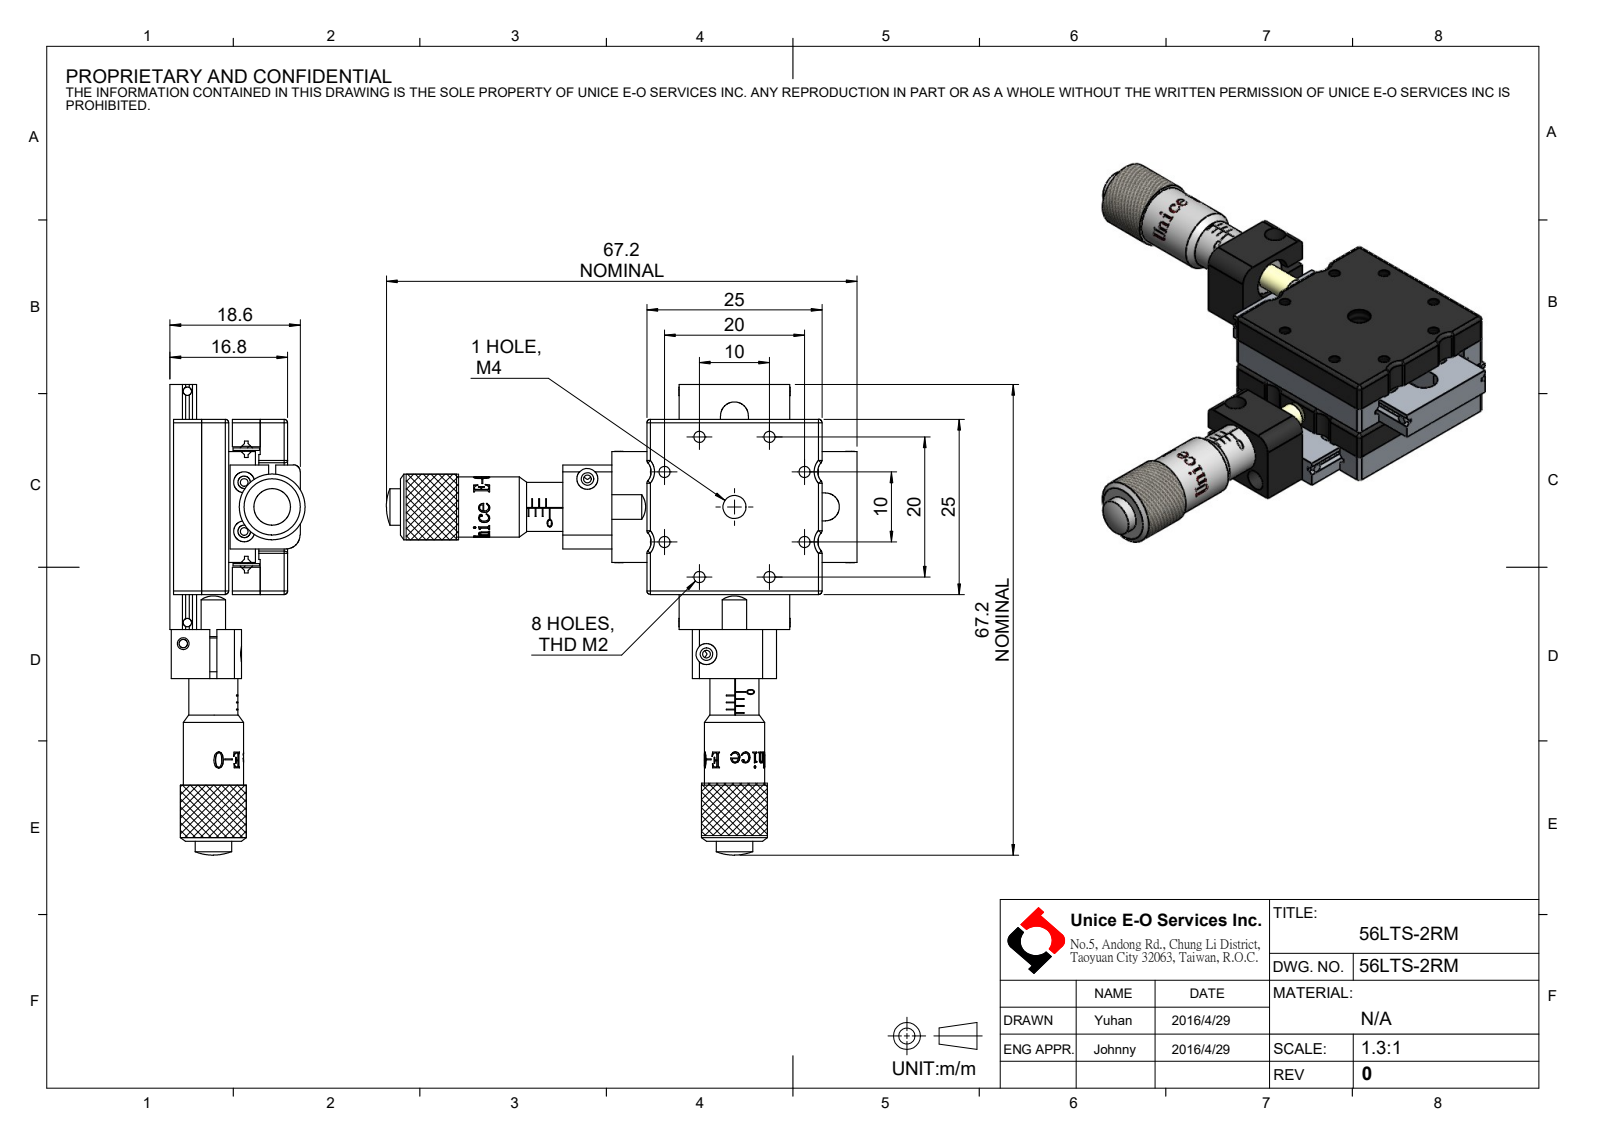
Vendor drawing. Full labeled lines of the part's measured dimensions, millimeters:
Part name (STEP PRODUCT): 56LTS-2RM
STEP written by: SolidWorks 2016 (CONFIG_CONTROL_DESIGN)
Units: millimetres
Bodies: 42 solids, 1664 faces (666 planar, 622 cylindrical, 376 other)
Overall size (bounding box): 67.2 × 67.2 × 19.3
Volume: 13 403 mm³ · Surface area: 16 109 mm²
Round holes (diameter × count): ⌀1.1 ×20, ⌀1.8 ×18, ⌀3.1 ×12, ⌀1.2 ×8, ⌀1.6 ×8, ⌀2.4 ×8, ⌀3 ×8, ⌀4 ×8, ⌀1.7 ×2, ⌀2.5 ×2, ⌀2.6 ×2, ⌀3.5 ×2
Round bosses / shafts (diameter × count): ⌀1.5 ×21, ⌀9.4 ×2, ⌀8.6 ×2, ⌀7 ×2, ⌀6.4 ×2, ⌀5.7 ×2, ⌀5.2 ×2, ⌀1.2 ×2
Partial cylindrical surfaces — rounded edges, fillets, slot ends (radius × count): R0.5 ×28, R0.75 ×14, R2 ×14, R1 ×2, R4.28 ×2
Main face-to-face distances: 8.4, 4.6, 3.8, 0.7, 3.9, 0.5, 4.3, 4.1, 4.5, 8.9
Hole centre spacings: 4.04, 5.03, 5.64, 9, 10.66, 11.18, 11.44, 13.87
